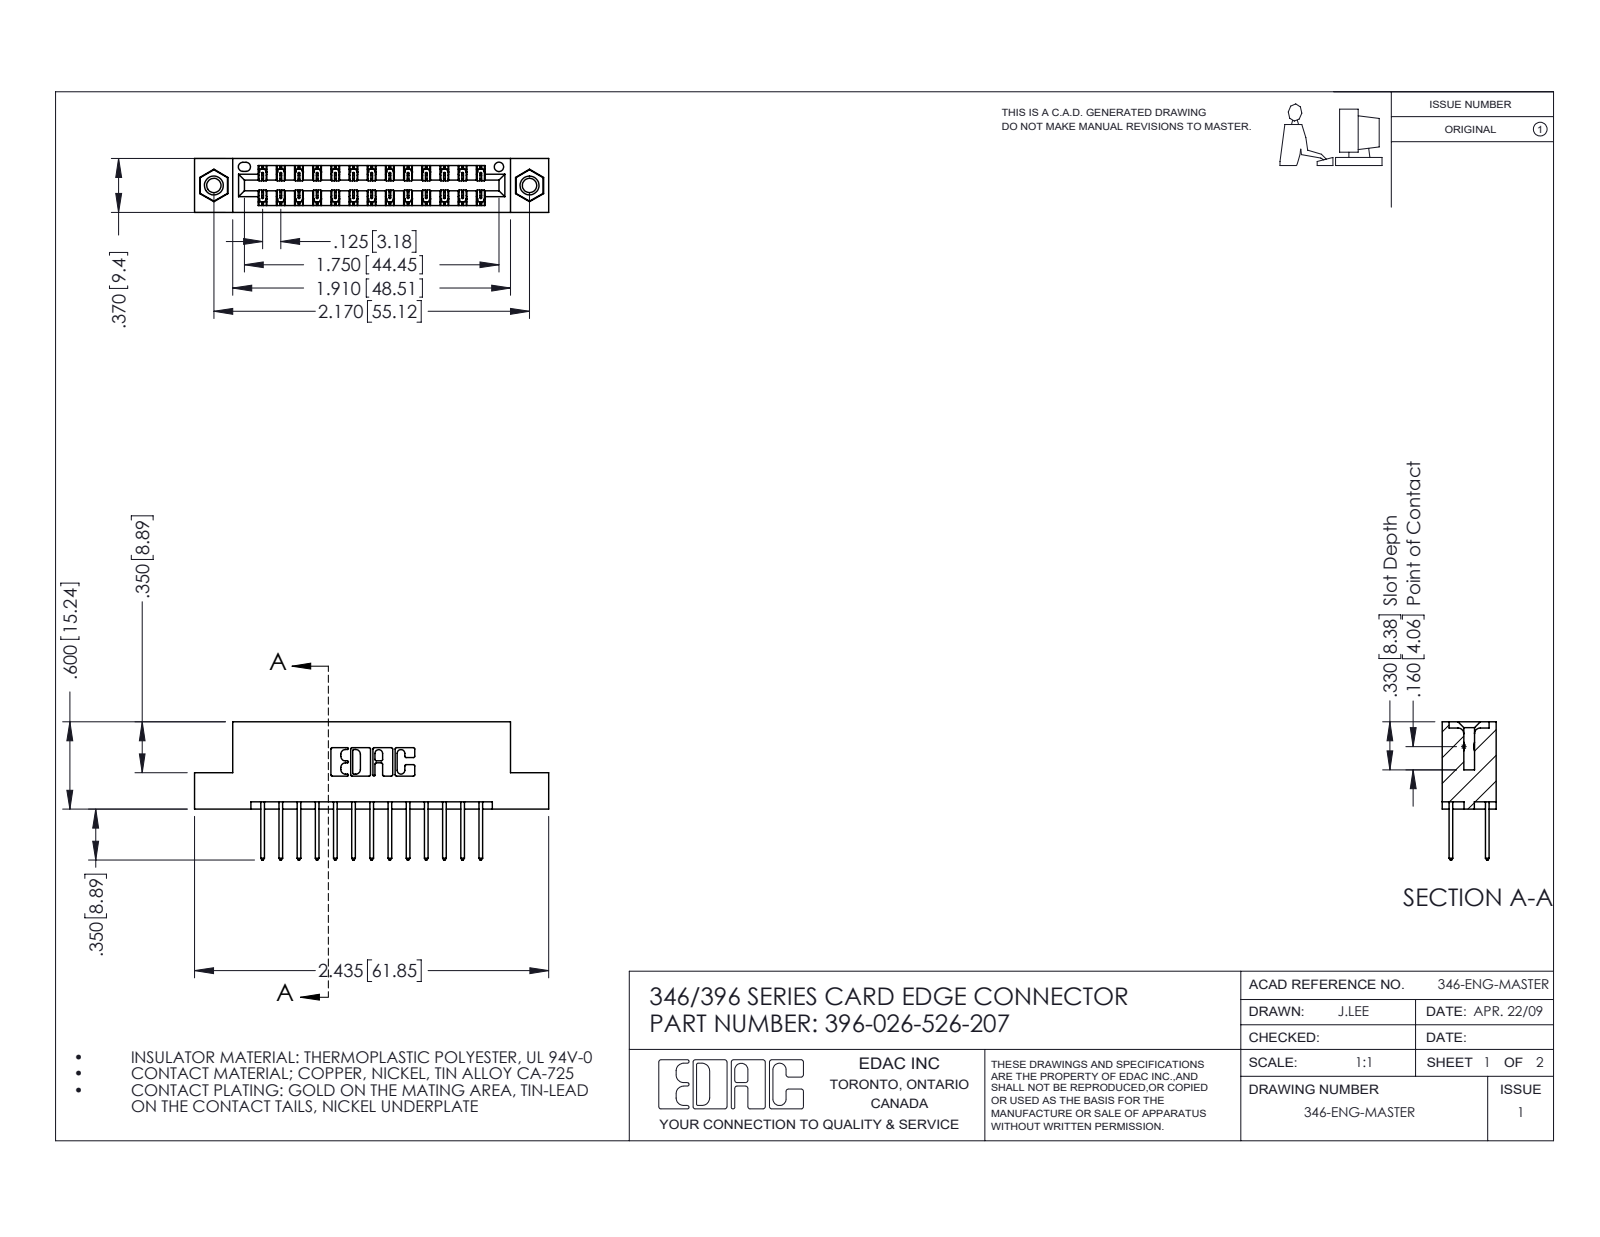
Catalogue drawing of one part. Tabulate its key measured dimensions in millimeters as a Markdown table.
| quantity | value |
| --- | --- |
| part name | 396-026-526-207; 345-250-001_345-250-005-103; 345-292-001_345-293-126; 346 Part_Flush Mounting Lugs - 0.156 Dia-TI |
| STEP written by | SolidWorks 2016 (CONFIG_CONTROL_DESIGN) |
| units | millimeters |
| bodies | 29 solids, 1534 faces (1018 planar, 500 cylindrical, 16 other) |
| overall size | 61.8 × 24.1 × 9.4 |
| volume | 5 830 mm³ |
| surface area | 7 787 mm² |
| round holes (diameter × count) | 2.5 × 2, 3.2 × 2, 4 × 2, 1.6 × 1 |
| round bosses / shafts (diameter × count) | 3.9 × 2 |
| partial cylindrical surfaces (radius × count) | 0.2 × 39, 0.3 × 26, 0.3 × 22, 0.2 × 6, 0.8 × 6, 0.7 × 3, 0.4 × 2, 0.6 × 2 |
| main face-to-face distances | 6.4, 1.2, 8.2, 9.4, 1.8, 7.6, 0.6, 7, 3.8, 5.6 |
| hole center spacings | 6.2, 49.9, 55.1 |
